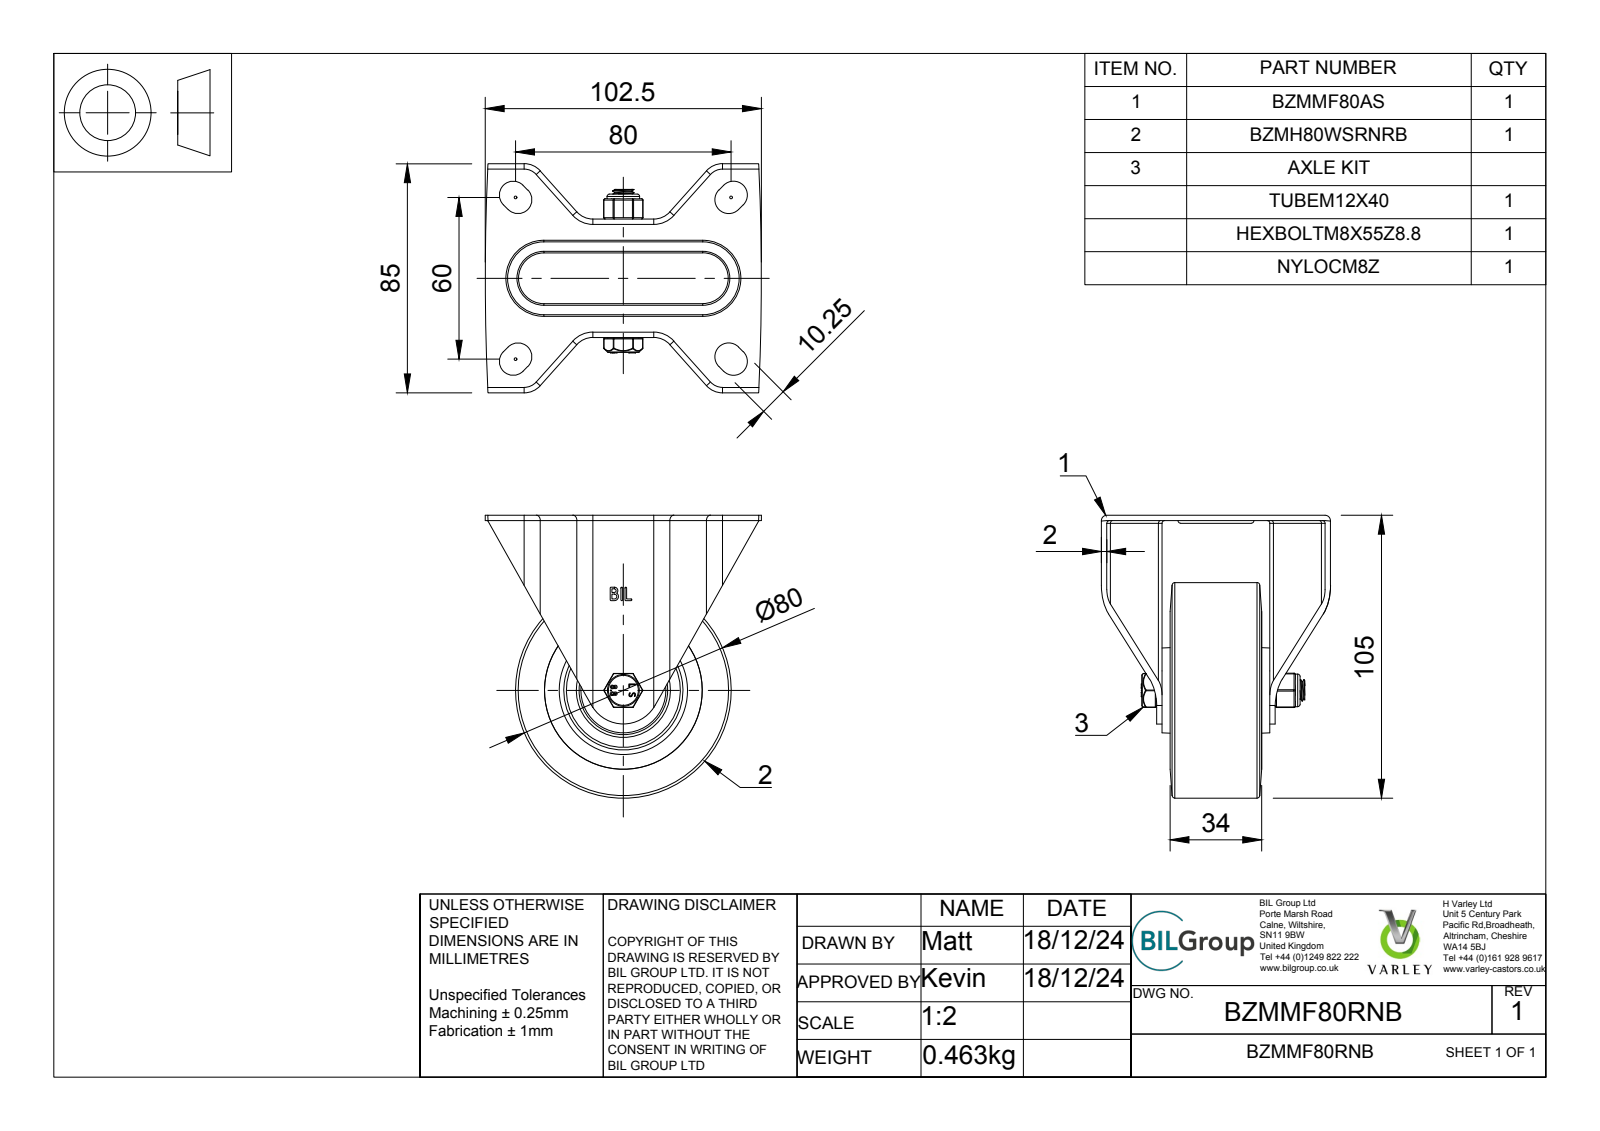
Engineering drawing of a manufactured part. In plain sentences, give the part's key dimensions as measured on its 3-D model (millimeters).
The part is named "BZMMF80RNB v3; BZMMF80AS - 40 v2; ZINC PLATED, PRESSED STEEL BRACKET; BZMH80WSRNRB v1 (+6 more)". Its 3-D file was written by "Autodesk Translation Framework v13.20.0.188 (AP242_MANAGED_MODEL_BASED_3D_ENGINEERING_MIM_LF)". It is 17 solids with 488 faces: 195 planar, 191 cylindrical and 102 other. Overall it measures 105 by 102.5 by 85 millimeters. Its volume is 182 846 cubic millimeters and its surface area 87 353 square millimeters. Round holes: 2 of diameter 0.66, 1 of diameter 8, 1 of diameter 8.25, 1 of diameter 8.4, 1 of diameter 8.6, 1 of diameter 12.5, 1 of diameter 12.6, 1 of diameter 20.5, 1 of diameter 24.8, 1 of diameter 58.5. Round bosses or shafts: 8 of diameter 3.75, 1 of diameter 80, 1 of diameter 24.6, 1 of diameter 20, 1 of diameter 12.1, 1 of diameter 11.9, 1 of diameter 11.5, 1 of diameter 7.87. Partial cylindrical surfaces (rounded edges, fillets, slot ends): 18 of radius 0.5, 12 of radius 0.25, 12 of radius 1, 8 of radius 2, 8 of radius 4, 8 of radius 5.12, 8 of radius 8, 4 of radius 0.33. The main face-to-face distances are 2, 5.16, 42, 40, 3.16, 3, 5, 7.16, 39, 37. The hole center spacings are 3.22, 2.49.
